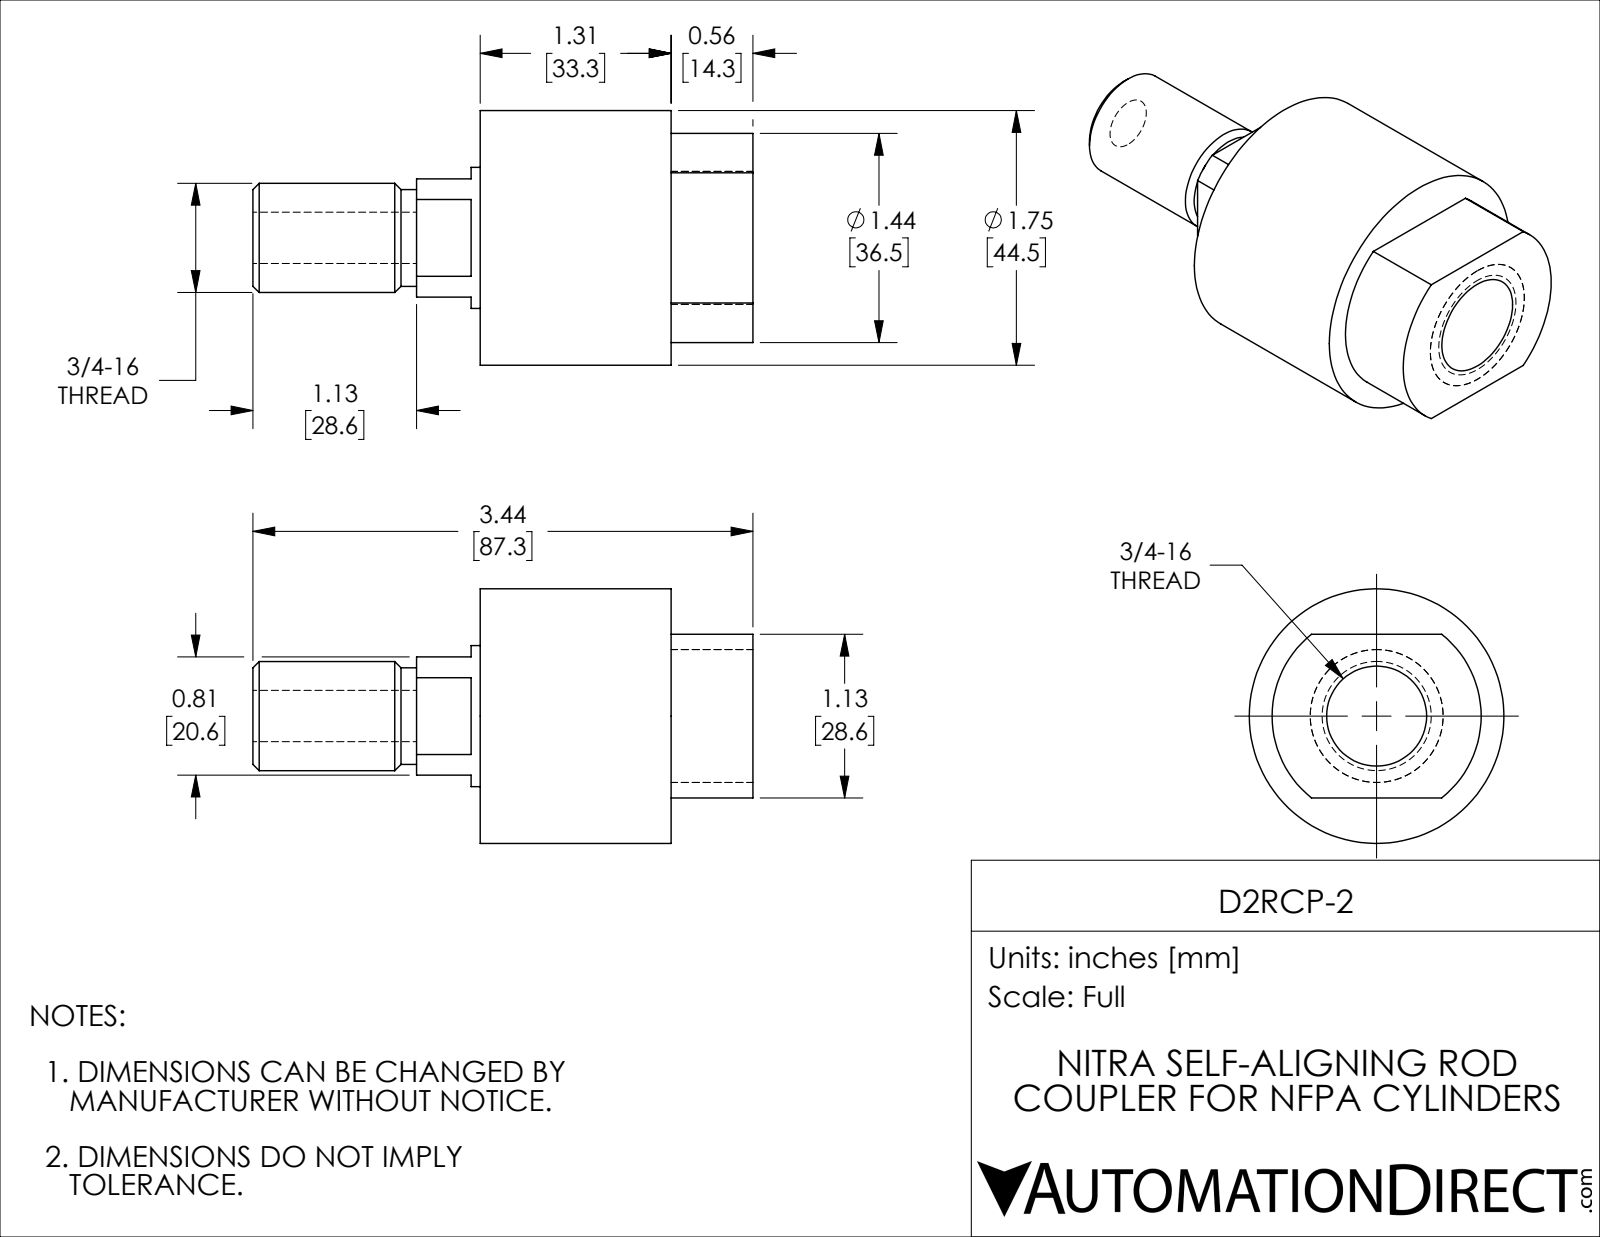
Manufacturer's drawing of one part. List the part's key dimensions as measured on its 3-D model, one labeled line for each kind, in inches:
Part name (STEP PRODUCT): D2RCP-2
STEP written by: SolidWorks 2019 (CONFIG_CONTROL_DESIGN)
Units: inches
Bodies: 1 solid, 34 faces (15 planar, 13 cylindrical, 6 other)
Overall size (bounding box): 3.437 × 1.75 × 1.75
Volume: 4.166 in³ · Surface area: 21.63 in²
Round holes (diameter × count): ⌀0.687 ×1
Round bosses / shafts (diameter × count): ⌀1.75 ×1, ⌀0.969 ×1, ⌀0.75 ×1, ⌀0.665 ×1
Partial cylindrical surfaces — rounded edges, fillets, slot ends (radius × count): R0.719 ×1
Main face-to-face distances: 1.875, 0.563, 1.312, 1.125, 0.156, 0.969, 0.813, 3.437, 2.874, 1.563
